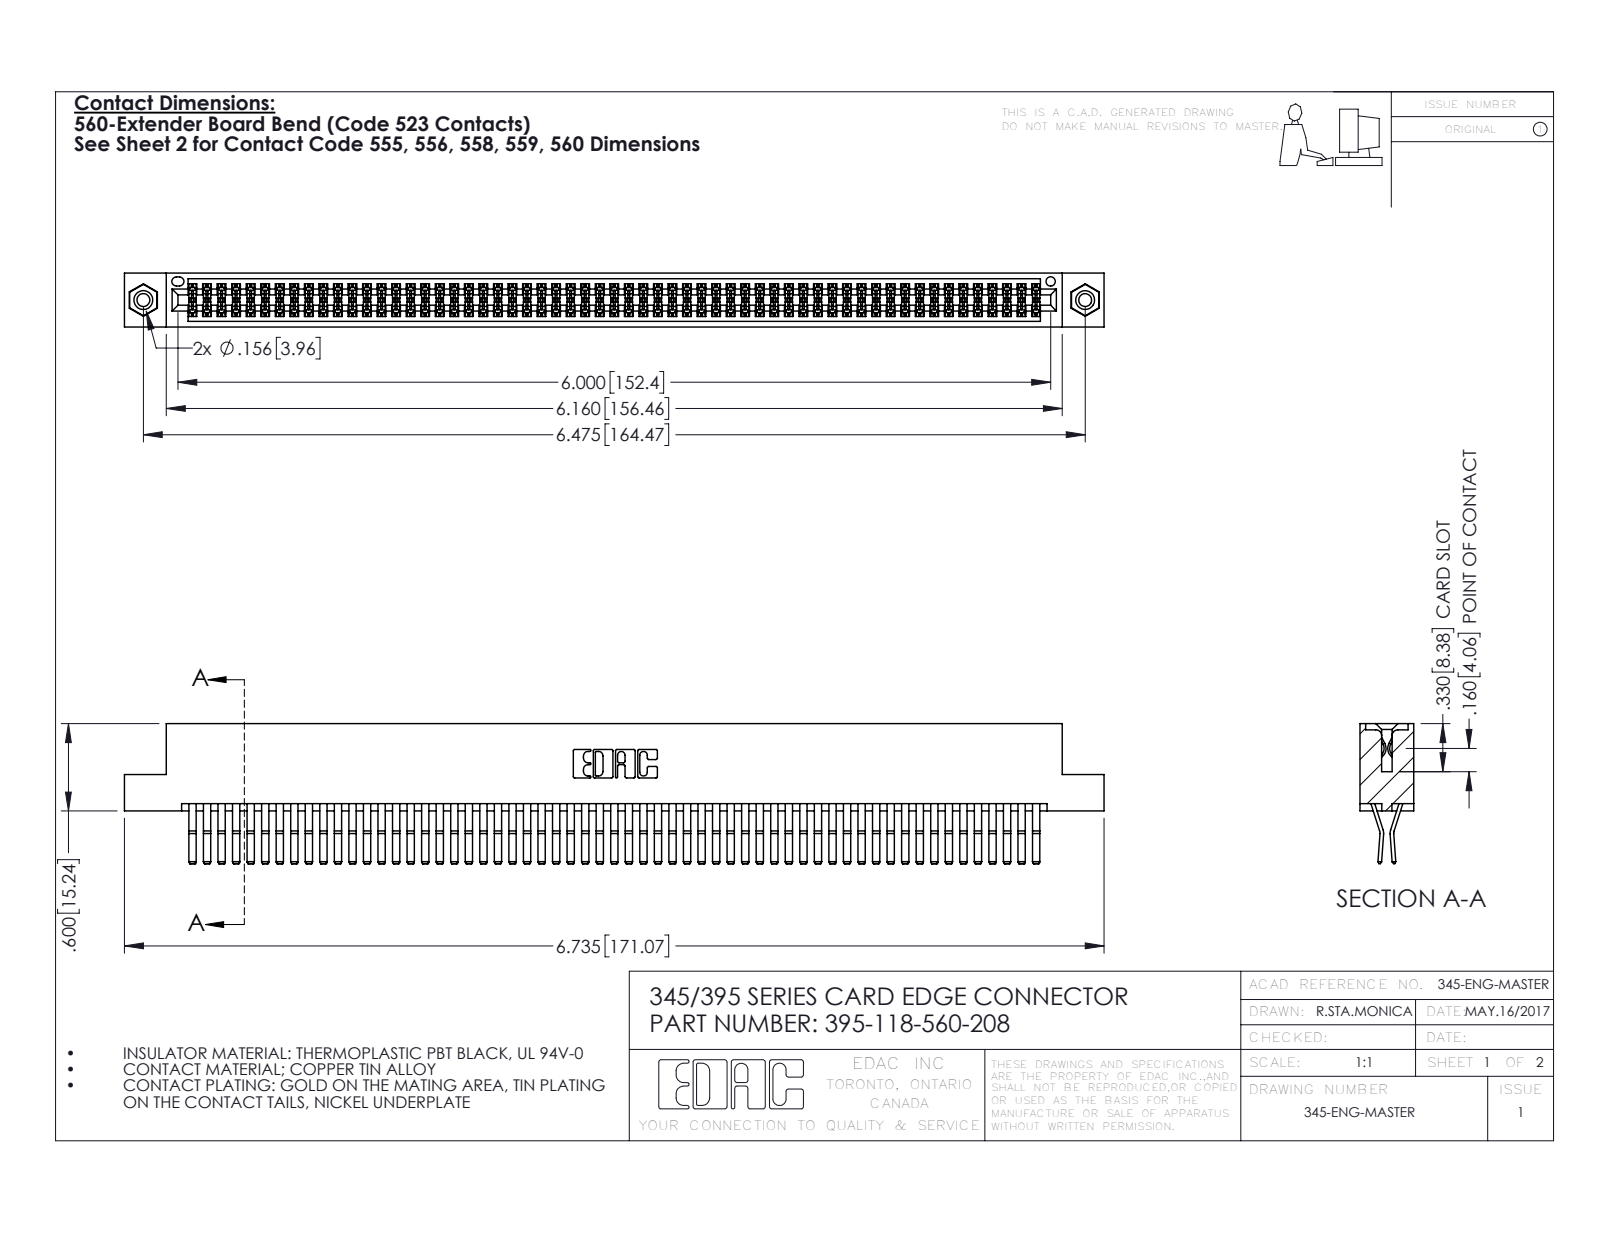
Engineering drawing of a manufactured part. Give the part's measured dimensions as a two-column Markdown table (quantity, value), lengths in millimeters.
| quantity | value |
| --- | --- |
| part name | 395-118-560-208; 345-250-001_345-250-003-102; 345-292-001_560 Tail; 345 Part_Flush Mounting Lugs - 0.156 Dia-TI |
| STEP written by | SolidWorks 2016 (CONFIG_CONTROL_DESIGN) |
| units | millimeters |
| bodies | 121 solids, 6322 faces (4006 planar, 2300 cylindrical, 16 other) |
| overall size | 171.1 × 24.4 × 9.4 |
| volume | 17 550 mm³ |
| surface area | 28 260 mm² |
| round holes (diameter × count) | 2.3 × 2, 3.2 × 2, 4 × 2, 1.6 × 1 |
| round bosses / shafts (diameter × count) | 3.9 × 2 |
| partial cylindrical surfaces (radius × count) | 0.2 × 177, 0.3 × 22, 0.2 × 6, 0.8 × 6, 0.7 × 3, 0.3 × 2, 0.4 × 2, 0.5 × 2 |
| main face-to-face distances | 0.6, 1.8, 7.6, 9.4, 5.1, 2.5, 6.9, 5.7, 4.4, 3.8 |
| hole center spacings | 6.9, 158.5, 164.5 |
